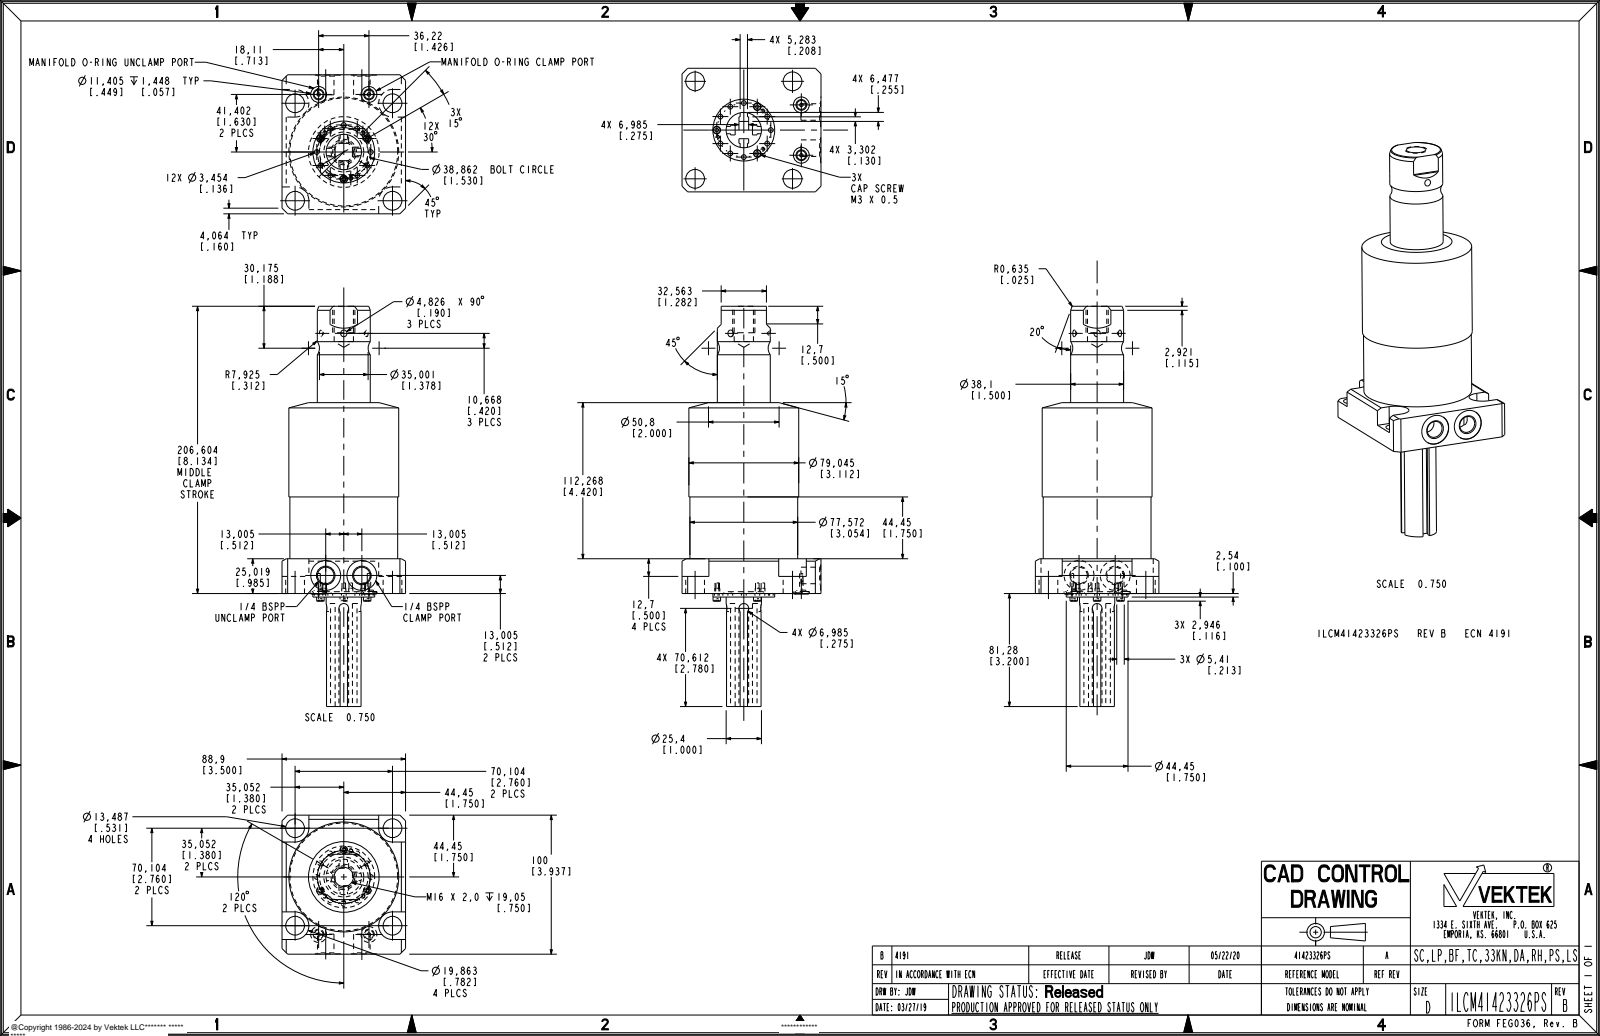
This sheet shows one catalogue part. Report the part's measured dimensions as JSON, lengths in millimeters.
{"part_name": "ILCM41423326PS", "step_written_by": "PRO/ENGINEER BY PARAMETRIC TECHNOLOGY CORPORATION, 2013320 (AUTOMOTIVE_DESIGN)", "units": "millimeters", "bodies": {"solids": 1, "faces": 279, "planar": 131, "cylindrical": 114, "other": 34}, "overall_size": [287.88, 100, 88.9], "volume_mm3": 834054, "surface_area_mm2": 80886, "round_holes": [[3.45, 12], [2.54, 6], [13.49, 4], [2.49, 2], [6.5, 2], [11.4, 2], [11.89, 2], [21.49, 2], [13.87, 1], [28.7, 1]], "round_bosses_or_shafts": [[3, 6], [5.41, 3], [79.05, 1], [77.57, 1], [44.45, 1], [38.1, 1], [25.4, 1], [18.26, 1]], "partial_cylinders_radius": [[9.93, 4], [0.76, 2], [3.49, 2]], "face_to_face_distances": [25.02, 2.73, 9.71, 88.9, 3.58, 8.86, 0.85, 6.13, 50.67, 38.23], "hole_center_spacings": [19.43, 33.66, 10.06, 19.44, 37.54, 27.49, 31.2, 38.37]}
